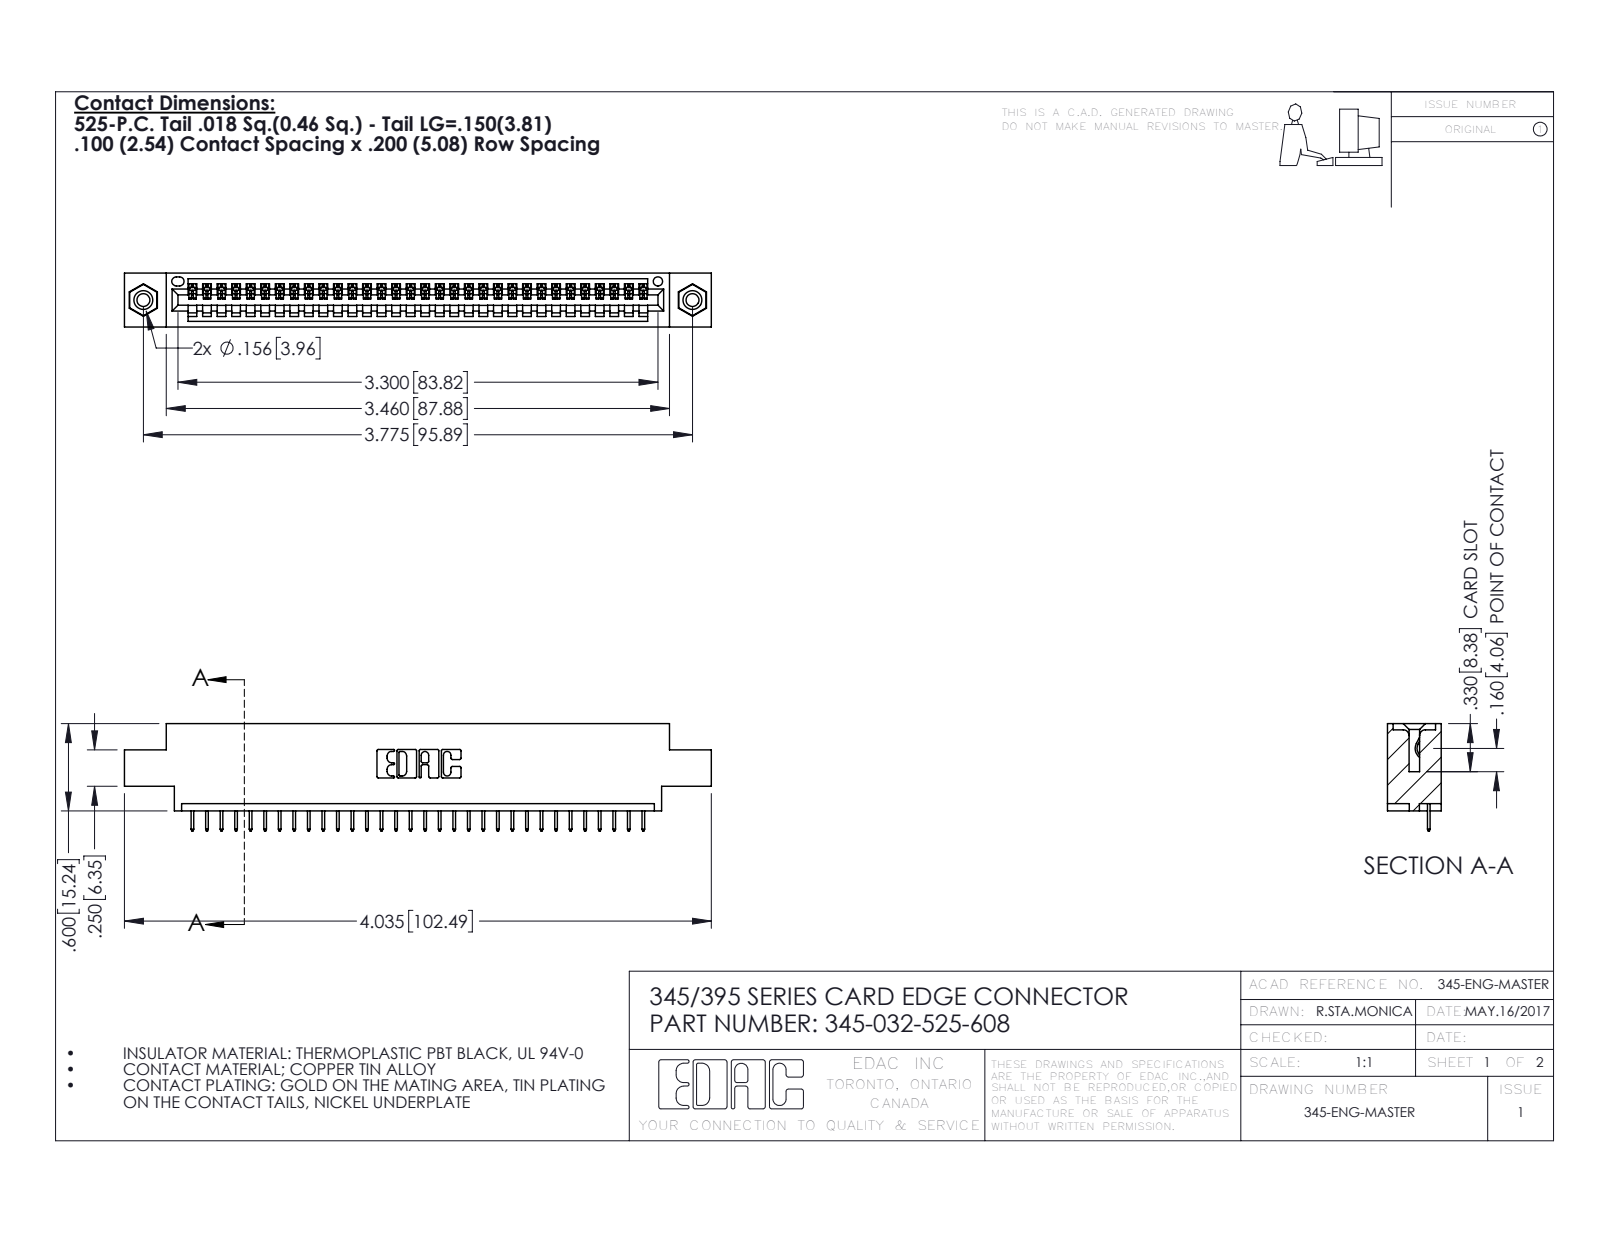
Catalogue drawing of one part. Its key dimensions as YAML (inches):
part_name: "345-292-001_345-293-125; 345-032-525-608; 345 Part_0.170 Offset - 0.156 Dia-TI; 345-250-001_345-250-003-102"
step_written_by: "SolidWorks 2020 (CONFIG_CONTROL_DESIGN)"
units: inches
bodies: {solids: 35, faces: 2174, planar: 1588, cylindrical: 570, other: 16}
overall_size: [4.035, 0.737, 0.37]
volume: 0.574
surface_area: 18.71
round_holes:
  - {diameter: 0.089, count: 2}
  - {diameter: 0.125, count: 2}
  - {diameter: 0.156, count: 2}
  - {diameter: 0.064, count: 1}
round_bosses_or_shafts:
  - {diameter: 0.155, count: 2}
partial_cylinders:
  - {radius: 0.006, count: 64}
  - {radius: 0.01, count: 22}
  - {radius: 0.007, count: 6}
  - {radius: 0.031, count: 6}
  - {radius: 0.026, count: 3}
  - {radius: 0.031, count: 2}
  - {radius: 0.04, count: 2}
  - {radius: 0.014, count: 1}
face_to_face_distances: [0.072, 0.298, 0.37, 0.2, 0.098, 0.272, 0.025, 0.225, 0.175, 0.072]
hole_center_spacings: [0.27, 3.54, 3.775]
